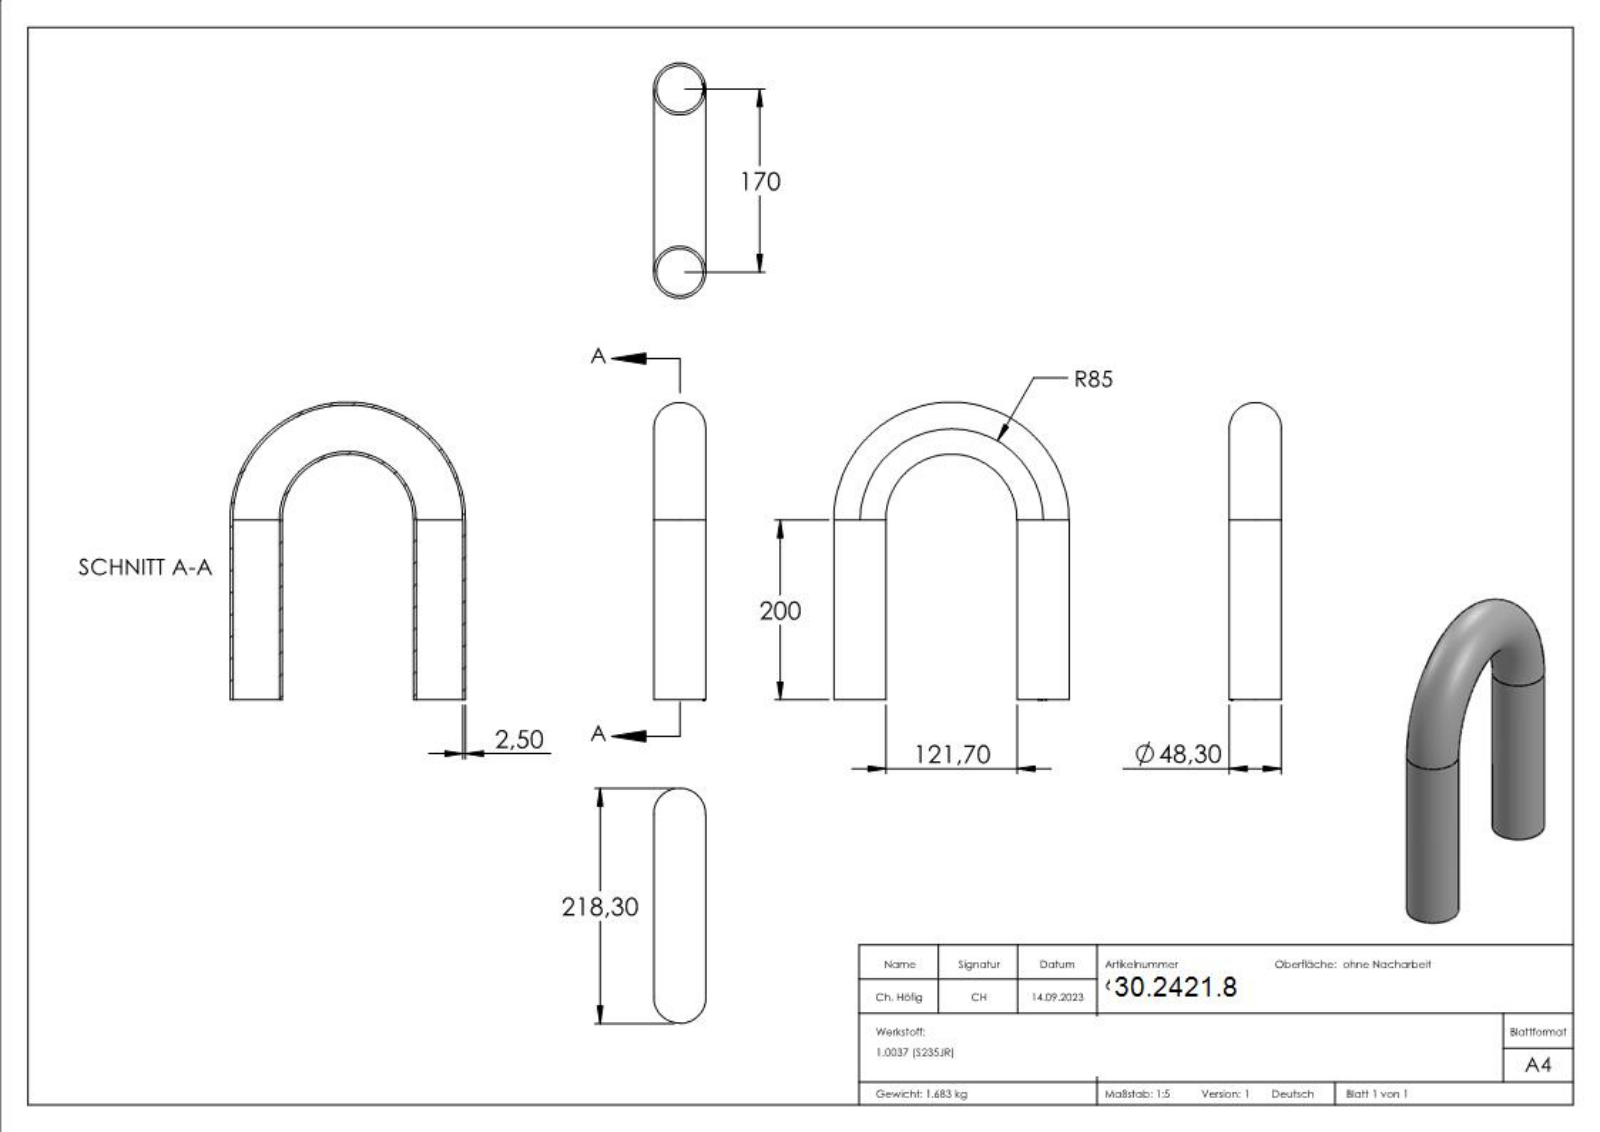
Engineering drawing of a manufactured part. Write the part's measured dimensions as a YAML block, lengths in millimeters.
part_name: "6968-180"
step_written_by: "SolidWorks 2018 (CONFIG_CONTROL_DESIGN)"
units: millimeters
bodies: {solids: 1, faces: 226, planar: 102, cylindrical: 4, other: 120}
overall_size: [275.63, 218.3, 48.3]
volume: 215827
surface_area: 173387
round_holes:
  - {diameter: 43.3, count: 2}
round_bosses_or_shafts:
  - {diameter: 48.3, count: 2}
face_to_face_distances: [0.4, 0.32, 0.51, 0.33, 0.47, 0.43, 0.44, 0.36, 0.8, 0.79]
hole_center_spacings: [170]
